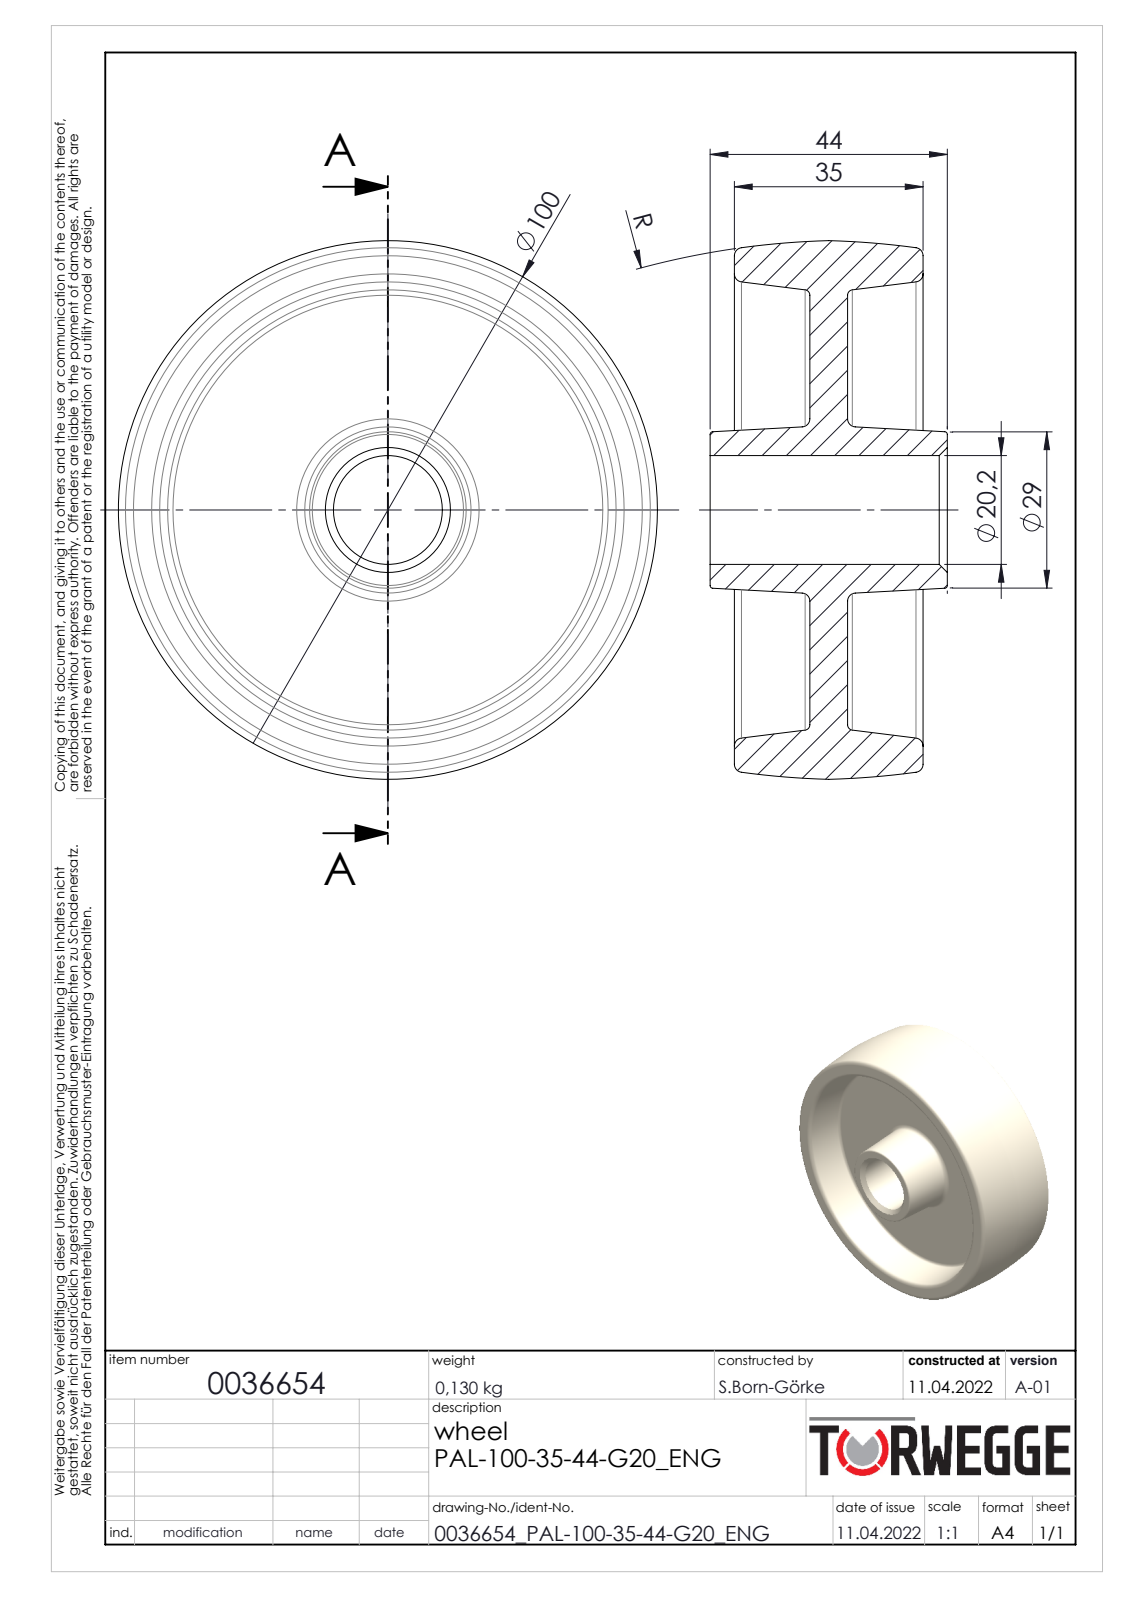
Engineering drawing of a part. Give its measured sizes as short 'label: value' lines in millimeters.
name: 0036654
written by: SolidWorks 2020 (AUTOMOTIVE_DESIGN)
unit: mm
bodies: 1 solid, 42 faces (6 planar, 2 cylindrical, 34 other)
size: 100 × 100 × 44
volume: 127 902 mm³; area: 36 717 mm²
holes: 1× ⌀20.2
face distances: 7, 14, 21, 35, 4.5, 18.5, 25.5, 39.5, 44
